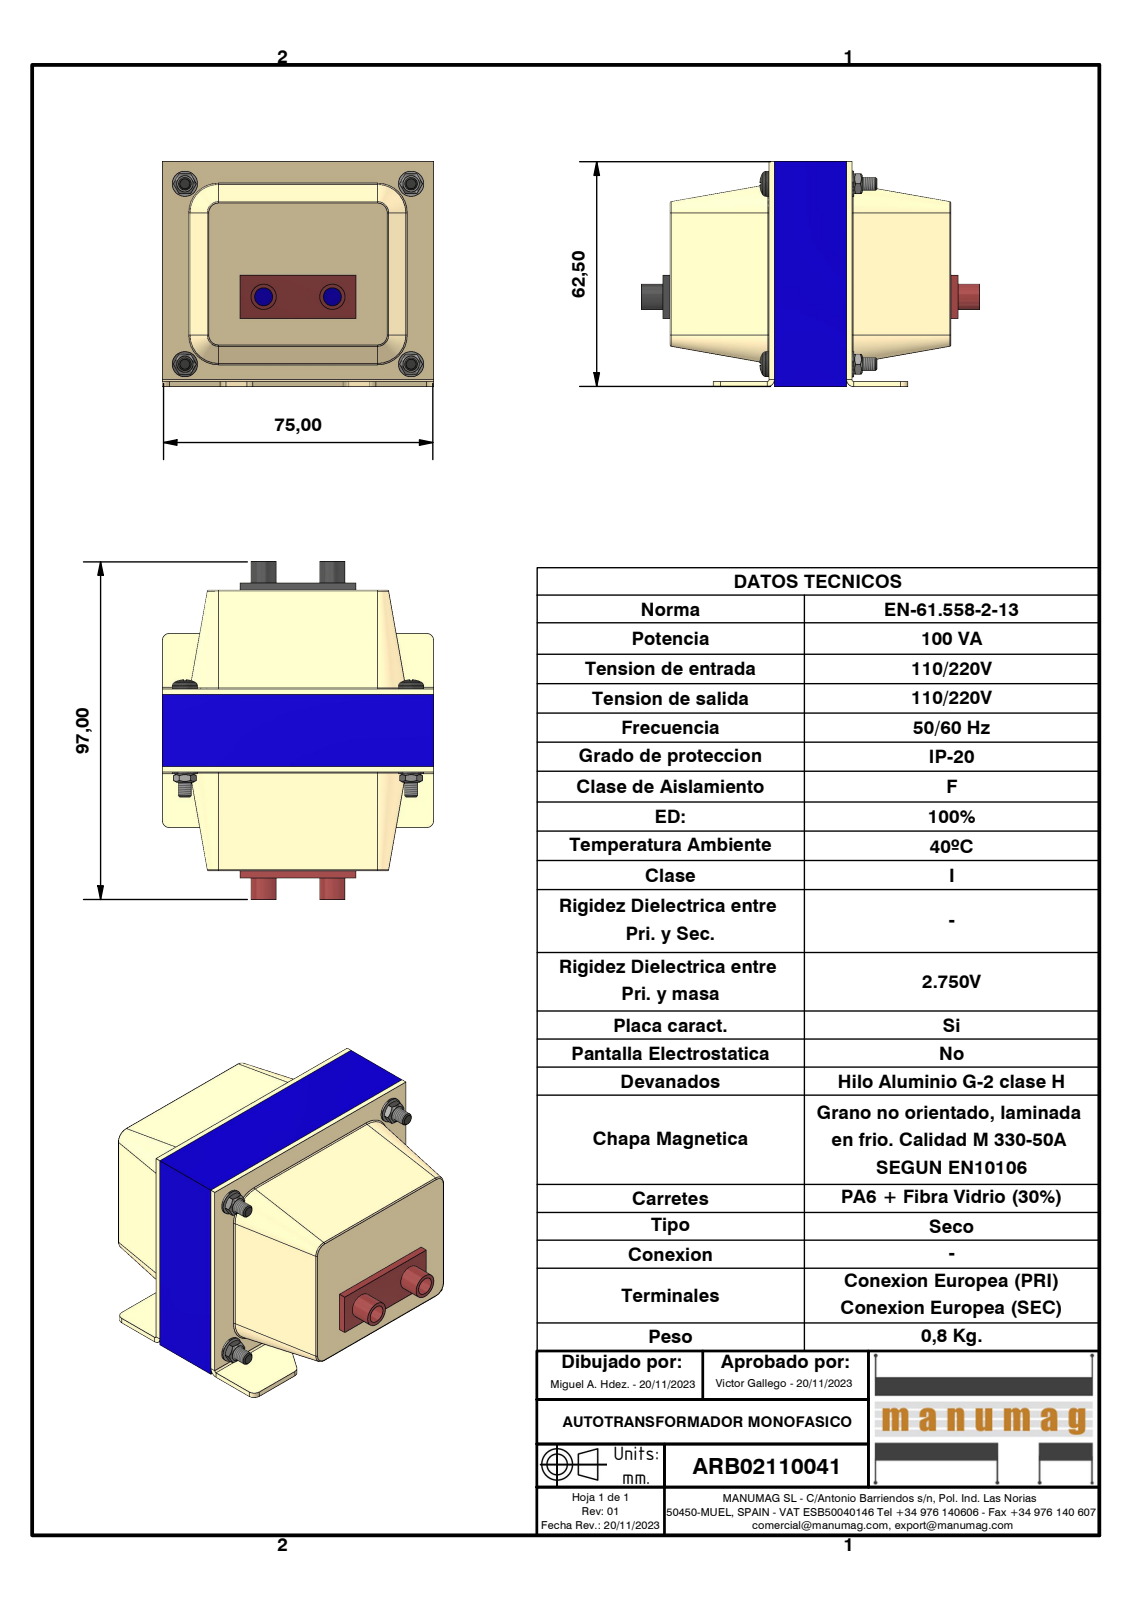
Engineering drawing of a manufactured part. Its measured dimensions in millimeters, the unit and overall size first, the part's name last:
Units: millimetres
Overall size (bounding box): 94 × 75 × 62.5
Round holes (diameter × count): ⌀2.46 ×4, ⌀3 ×4, ⌀3.2 ×4, ⌀4.5 ×4, ⌀5 ×2
Round bosses / shafts (diameter × count): ⌀7 ×6, ⌀3.5 ×4, ⌀3.18 ×4
Partial cylindrical surfaces — rounded edges, fillets, slot ends (radius × count): R0.38 ×16, R2 ×14, R0.5 ×2
Main face-to-face distances: 1.5, 49, 27.5, 20, 12.5, 29, 62.56, 52.71, 21.5, 50.5
Hole centre spacings: 28.67, 38.13, 44.83, 50, 51.4, 62.5, 80.04, 19
Volume: 92 410 mm³ · Surface area: 62 250 mm²
Bodies: 17 solids, 366 faces (170 planar, 72 cylindrical, 124 other)
Part name (STEP PRODUCT): ARB02110041; TAPA RC25 RECEPTACULO; Receptaculo negro; Receptaculo Rojo (+4 more)
STEP written by: Autodesk Inventor 2023 (AUTOMOTIVE_DESIGN)
